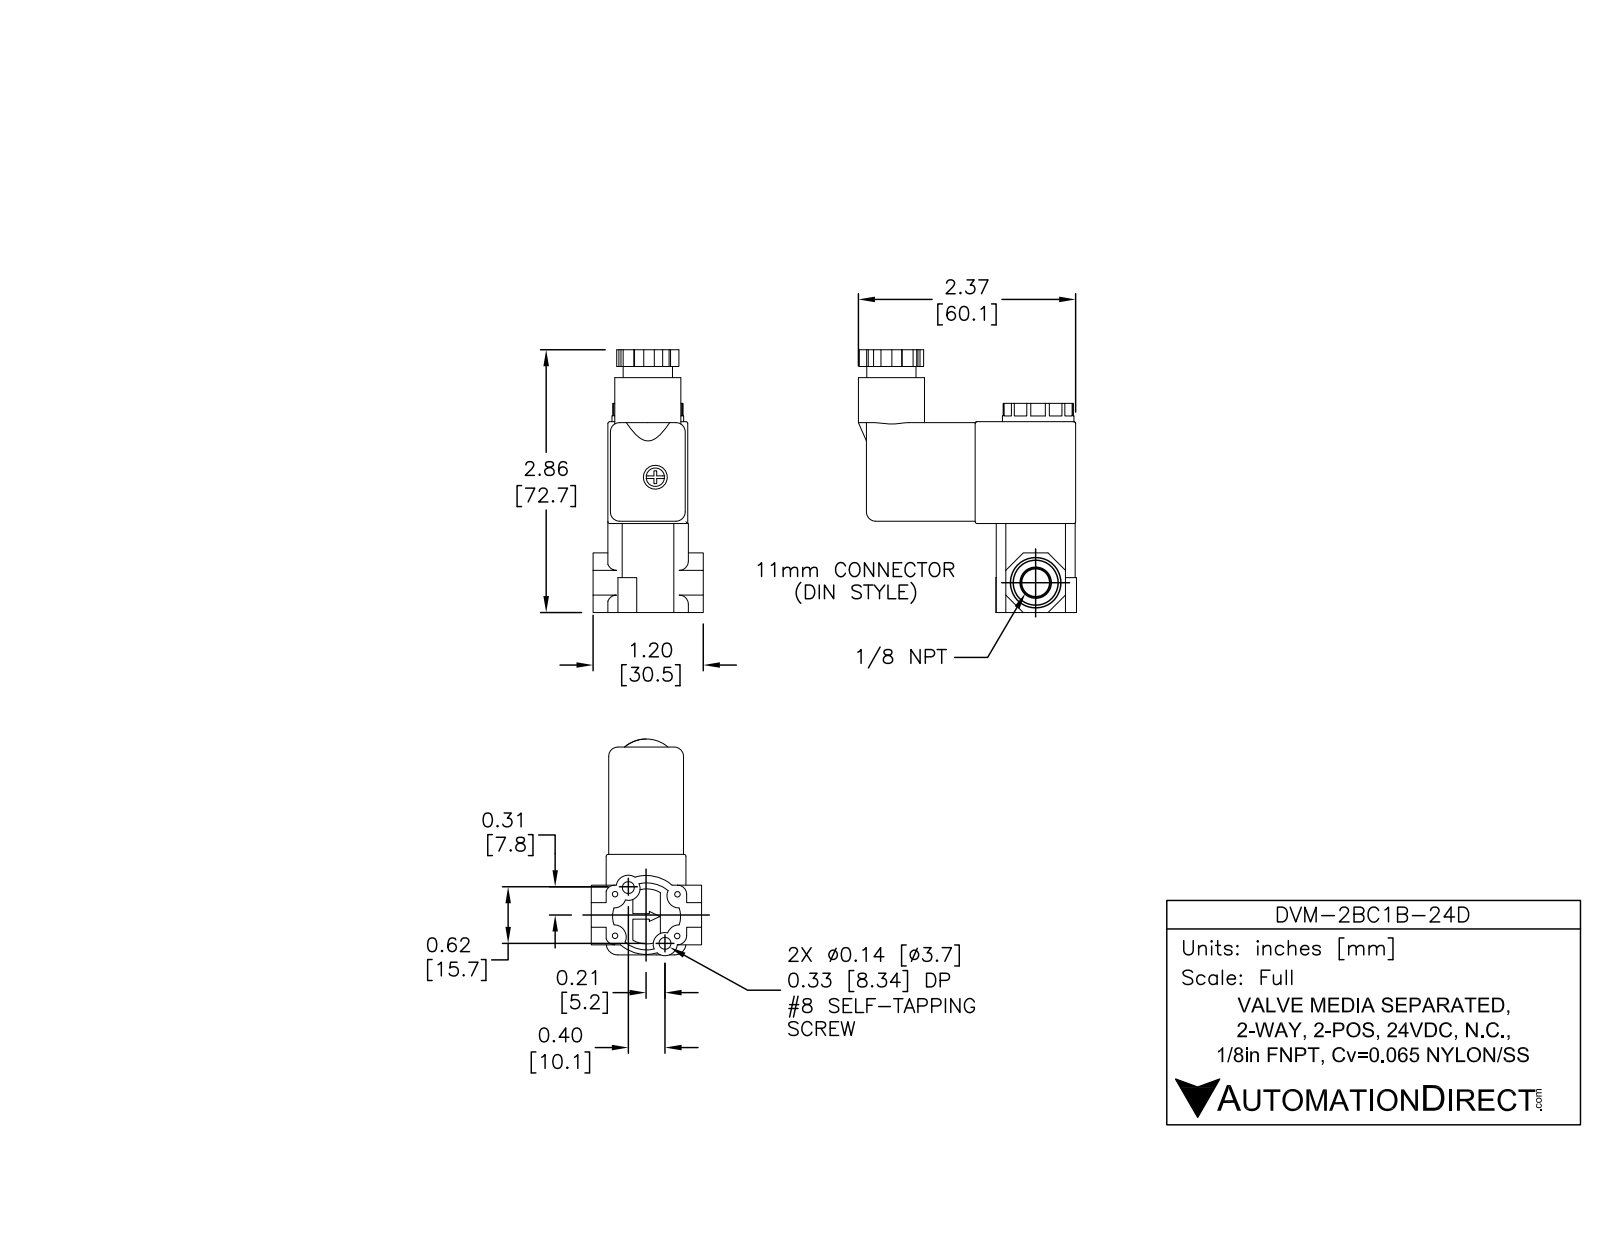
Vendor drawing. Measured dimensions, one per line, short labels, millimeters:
name: DVM-2BC1B-24D
written by: SolidWorks 2015 (AUTOMOTIVE_DESIGN)
unit: mm
bodies: 1 solid, 253 faces (133 planar, 101 cylindrical, 19 other)
size: 74 × 63.1 × 22.3
volume: 49 850 mm³; area: 12 840 mm²
holes: 2× ⌀3.2, 2× ⌀3.5, 2× ⌀3.5, 2× ⌀8.1, 1× ⌀6.4, 1× ⌀6.6, 1× ⌀10.4
bosses: 1× ⌀19.8, 1× ⌀18.3, 1× ⌀13.6, 1× ⌀6.4, 1× ⌀5.1
rounds: 12× R3.9, 11× R0.5, 11× R2.5, 4× R3.4, 2× R3.2, 2× R3.3, 2× R3.4, 2× R7
face distances: 0.7, 21.4, 22.1, 20.7, 57.2, 16.5, 5.1, 54.1, 33.9, 28.8
hole spacings: 11.4, 48.1, 4.4, 4.4, 8.6, 9.7, 9.7, 10
